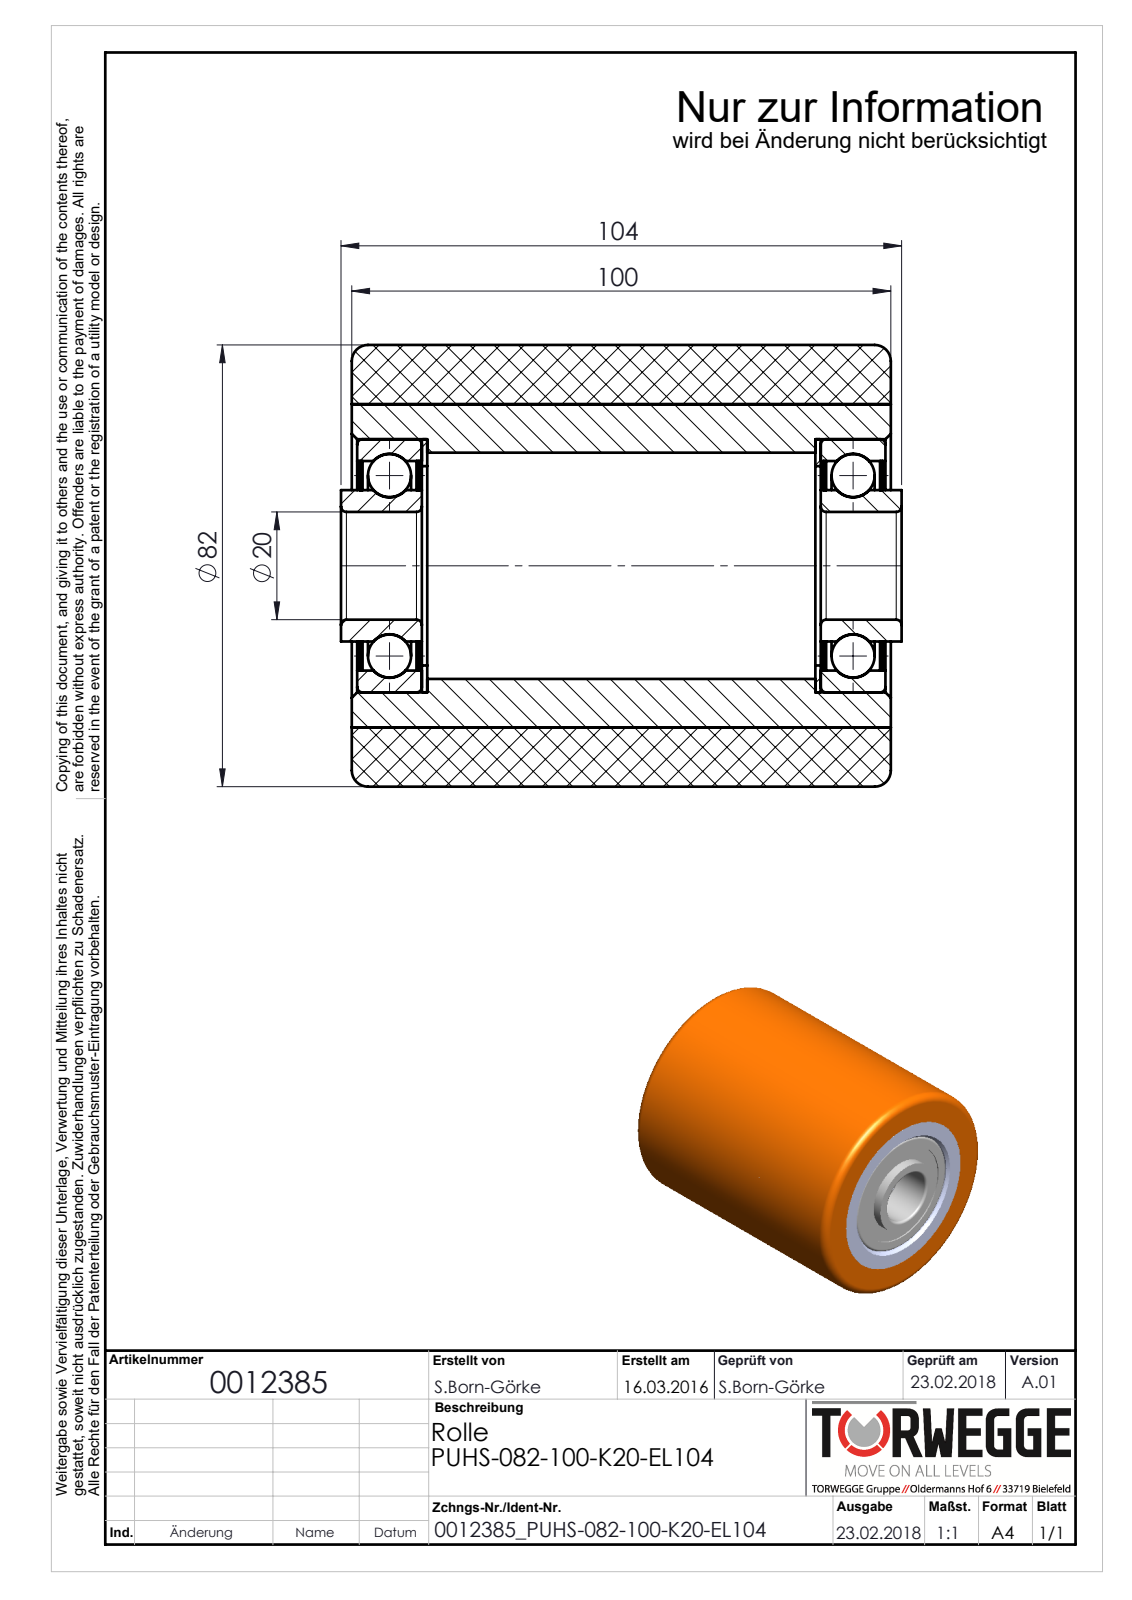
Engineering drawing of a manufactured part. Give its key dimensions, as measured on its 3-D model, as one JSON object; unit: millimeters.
{"part_name": "0012385_PUHS-082-100-K20-EL104", "step_written_by": "SolidWorks 2016 (AUTOMOTIVE_DESIGN)", "units": "millimeters", "bodies": {"solids": 0, "faces": 56, "planar": 10, "cylindrical": 26, "other": 20}, "overall_size": [104, 82, 82], "round_holes": [[20, 1], [38.9, 1], [42, 1], [47, 1], [60, 1]], "round_bosses_or_shafts": [[82, 1], [28.1, 1]], "face_to_face_distances": [100, 1.5, 98.5, 1, 99, 0.5, 97.5, 97, 2, 3]}
